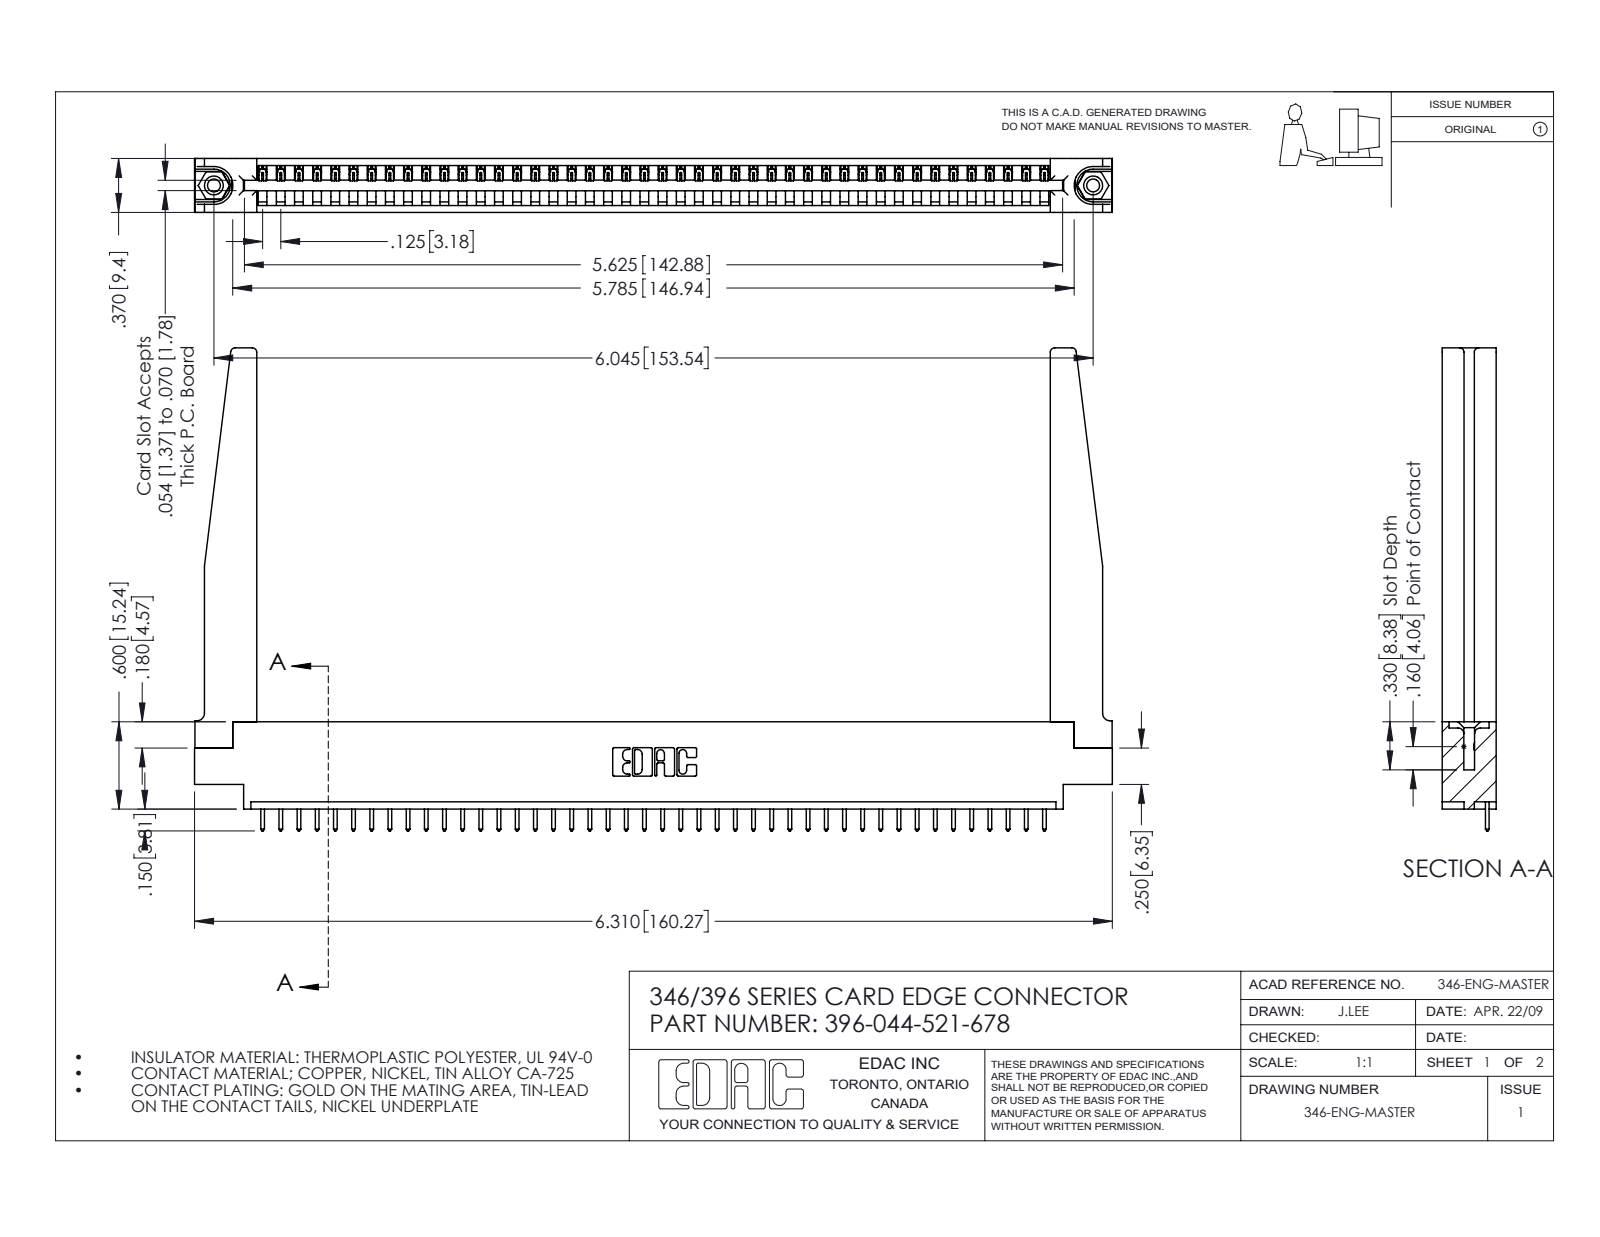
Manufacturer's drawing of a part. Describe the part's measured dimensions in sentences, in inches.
The part is named "346 Part_0.170 Offset - 0.156 Dia-TH; 396-044-521-678; 346-220-078_345-220-078; 345-250-001_345-250-001-102 (+1 more)". Its 3-D file was written by "SolidWorks 2016 (CONFIG_CONTROL_DESIGN)". It is 49 solids with 2912 faces: 1982 planar, 878 cylindrical and 52 other. Overall it measures 6.31 by 3.32 by 0.37 inches. Its volume is 1.342 cubic inches and its surface area 38.85 square inches. Round holes: 2 of diameter 0.089, 2 of diameter 0.125, 2 of diameter 0.156, 1 of diameter 0.064. Round bosses or shafts: 2 of diameter 0.155. Partial cylindrical surfaces (rounded edges, fillets, slot ends): 88 of radius 0.006, 88 of radius 0.01, 22 of radius 0.01, 8 of radius 0.03, 6 of radius 0.007, 6 of radius 0.031, 3 of radius 0.026, 2 of radius 0.031. The main face-to-face distances are 0.37, 0.048, 0.322, 0.072, 0.148, 0.15, 0.25, 0.298, 0.025, 0.222. The hole center spacings are 0.246, 5.836, 6.045.
